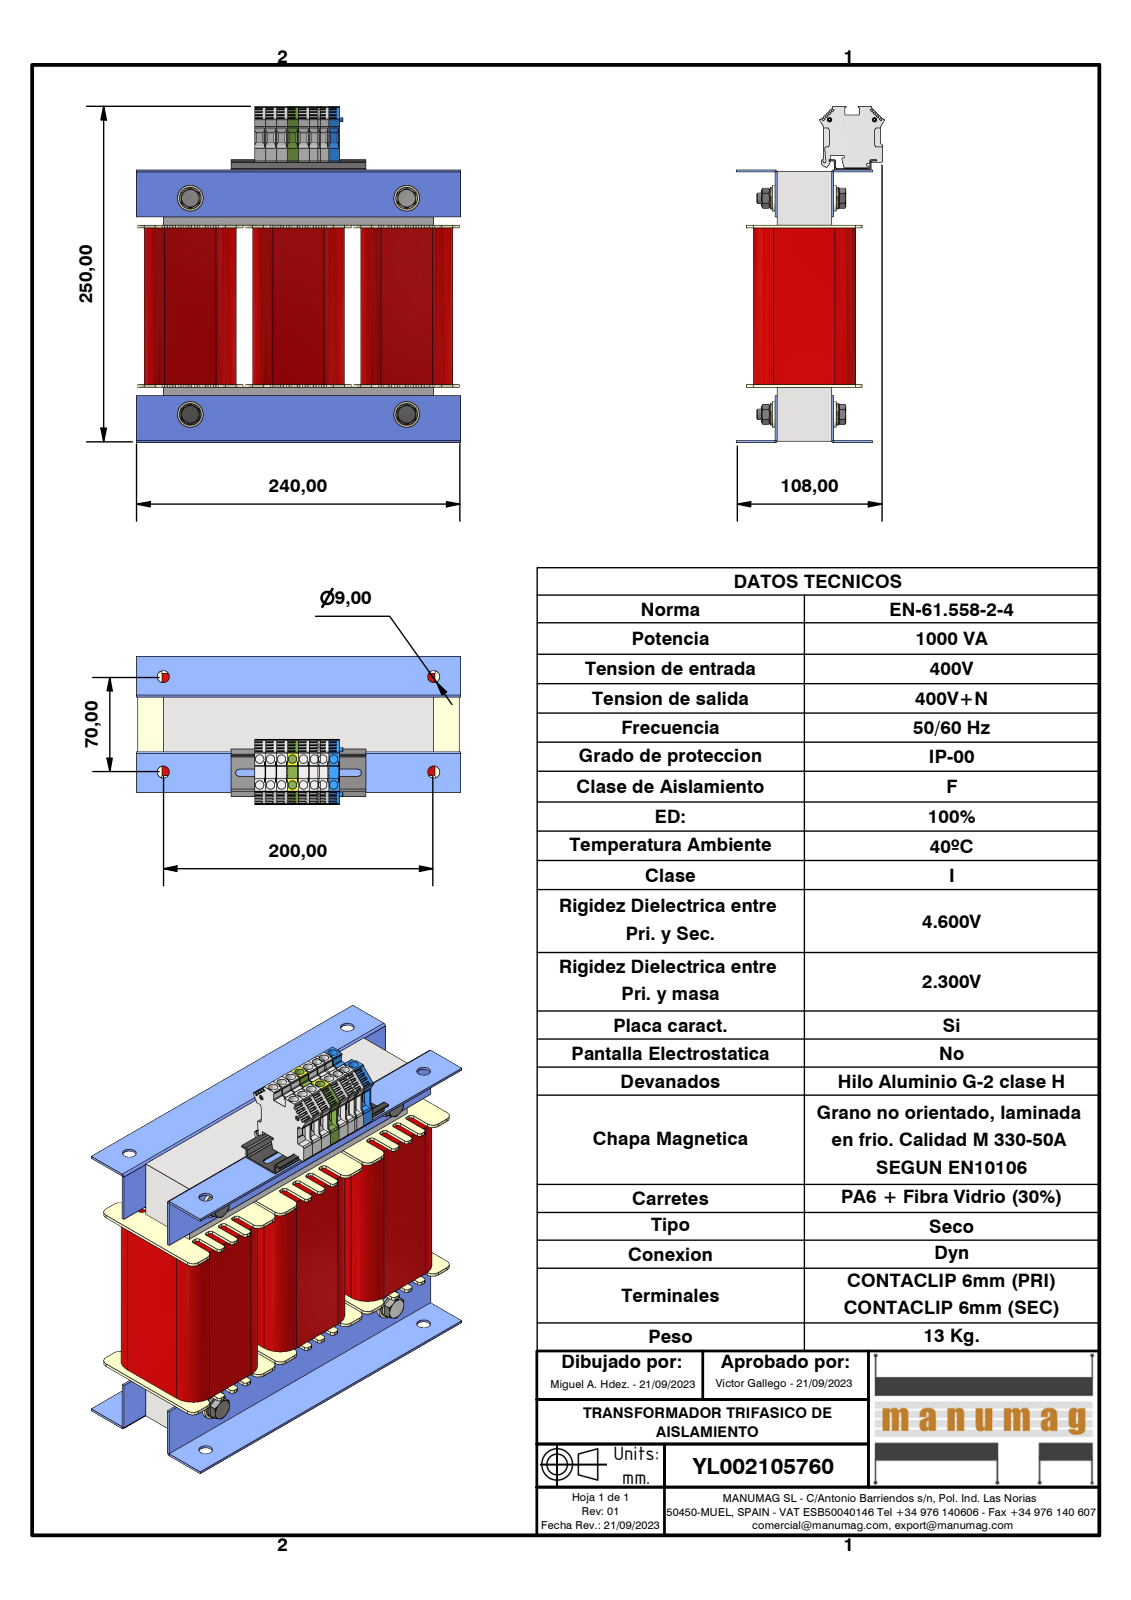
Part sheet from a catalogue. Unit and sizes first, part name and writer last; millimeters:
Units: millimetres
Overall size (bounding box): 249.05 × 240 × 109
Round holes (diameter × count): ⌀6.3 ×16, ⌀6.65 ×4, ⌀8 ×4, ⌀8.4 ×4, ⌀9 ×4, ⌀10.5 ×4, ⌀11 ×4, ⌀2.4 ×2, ⌀2.5 ×2, ⌀2.75 ×2, ⌀2.95 ×2
Round bosses / shafts (diameter × count): ⌀19 ×4, ⌀16 ×4, ⌀11.4 ×4, ⌀9.6 ×4, ⌀7.32 ×4
Partial cylindrical surfaces — rounded edges, fillets, slot ends (radius × count): R2 ×85, R5 ×24, R0.25 ×16, R1 ×15, R15 ×12, R2.6 ×8, R0.3 ×5, R0.5 ×5
Main face-to-face distances: 40, 1.5, 80, 160, 41.5, 120, 14, 54, 43, 161
Hole centre spacings: 8.1, 20.65, 16.2, 19, 24.97, 24.3, 30.85, 14.25
Volume: 2 615 000 mm³ · Surface area: 518 690 mm²
Bodies: 41 solids, 2898 faces (2018 planar, 712 cylindrical, 168 other)
Part name (STEP PRODUCT): YL002105760; 3UI120 200 x 200 - 40 (Rc40); UI 120_40; RC40 NT040 (+8 more)
STEP written by: Autodesk Inventor 2023 (AUTOMOTIVE_DESIGN)
